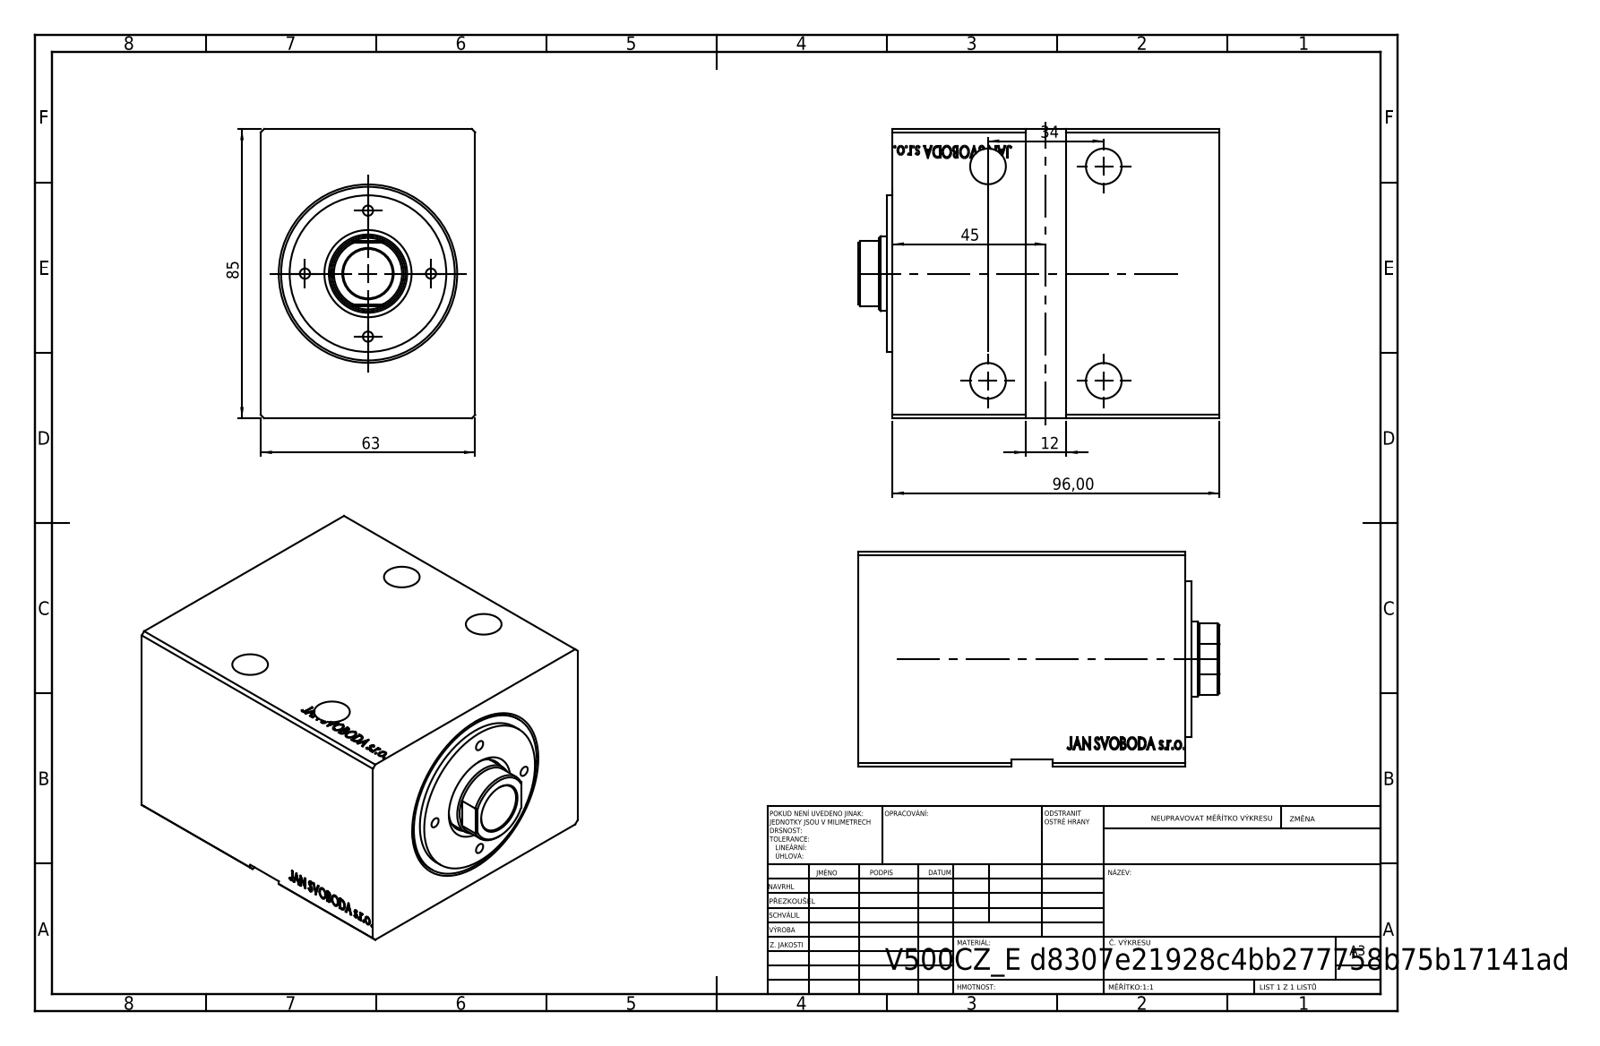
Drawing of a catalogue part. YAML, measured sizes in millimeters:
step_written_by: "SolidWorks 2019 (CONFIG_CONTROL_DESIGN)"
units: millimeters
bodies: {solids: 1, faces: 755, planar: 375, cylindrical: 14, other: 366}
overall_size: [96, 85, 63]
volume: 331792
surface_area: 59588
round_holes:
  - {diameter: 10.5, count: 4}
  - {diameter: 36, count: 1}
  - {diameter: 40, count: 1}
  - {diameter: 51, count: 1}
face_to_face_distances: [63, 85, 96, 81.3, 14.7, 2, 61, 95.8, 14.5, 25]
hole_center_spacings: [34, 63, 71.59]
